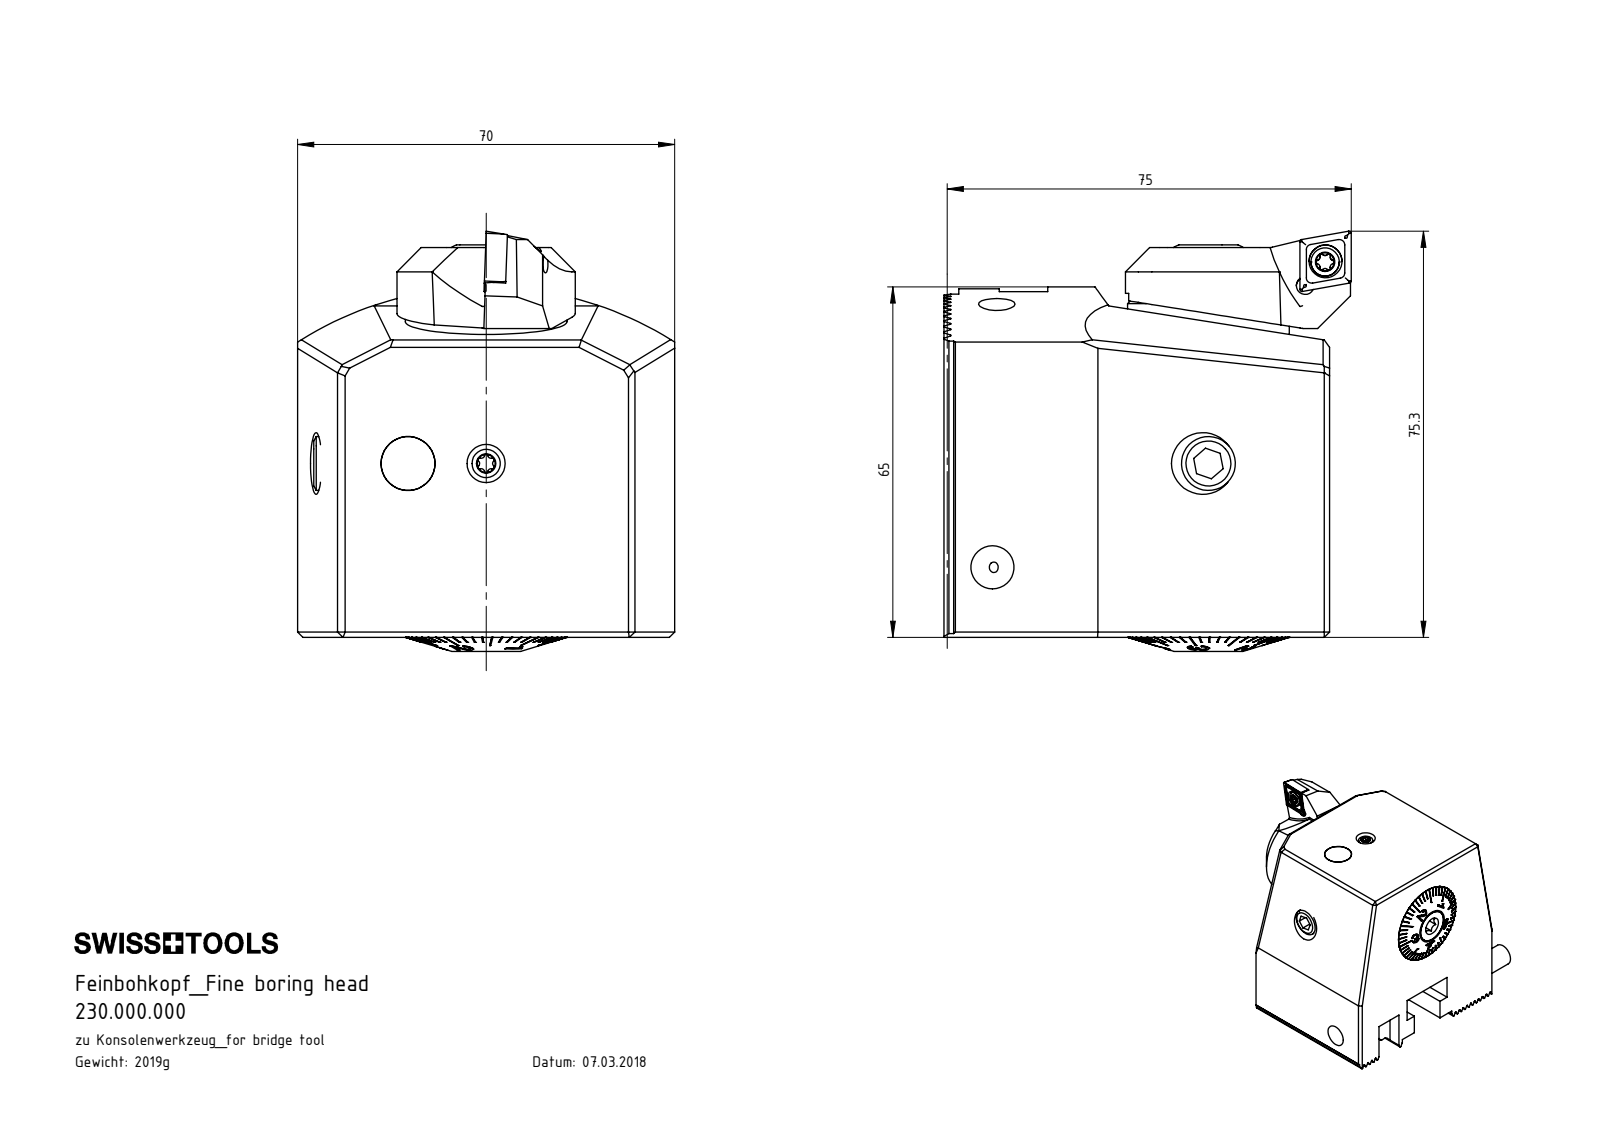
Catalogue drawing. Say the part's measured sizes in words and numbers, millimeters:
The part is named "ISO 4028 - M8 x 35; WCB-ER2.001.009_A; VK1-F0U.AA3.075_A; VK1.F0U.AA4.075 (+8 more)". Its 3-D file was written by "SolidWorks 2017 (AUTOMOTIVE_DESIGN)". It is 15 solids with 968 faces: 624 planar, 102 cylindrical and 242 other. Overall it measures 82 by 74.7 by 71.58 millimeters. Its volume is 238 219 cubic millimeters and its surface area 56 300 square millimeters. Round holes: 3 of diameter 8, 2 of diameter 3.3, 2 of diameter 8.5, 1 of diameter 4.2, 1 of diameter 6.8, 1 of diameter 10, 1 of diameter 11.4, 1 of diameter 12, 1 of diameter 12.4, 1 of diameter 13, 1 of diameter 14, 1 of diameter 20. Round bosses or shafts: 2 of diameter 10, 1 of diameter 30, 1 of diameter 29.98, 1 of diameter 29.9, 1 of diameter 25, 1 of diameter 18, 1 of diameter 16, 1 of diameter 11.95. Partial cylindrical surfaces (rounded edges, fillets, slot ends): 22 of radius 0.14, 6 of radius 0.34, 6 of radius 0.5, 6 of radius 0.59, 6 of radius 2.5, 4 of radius 2, 3 of radius 3.2, 1 of radius 0.8. The main face-to-face distances are 58, 6, 64, 1.73, 5.2, 8.66, 6.93, 3.46, 52.33, 18.5. The hole center spacings are 7, 14.5, 44.08, 44.55, 48.03.
